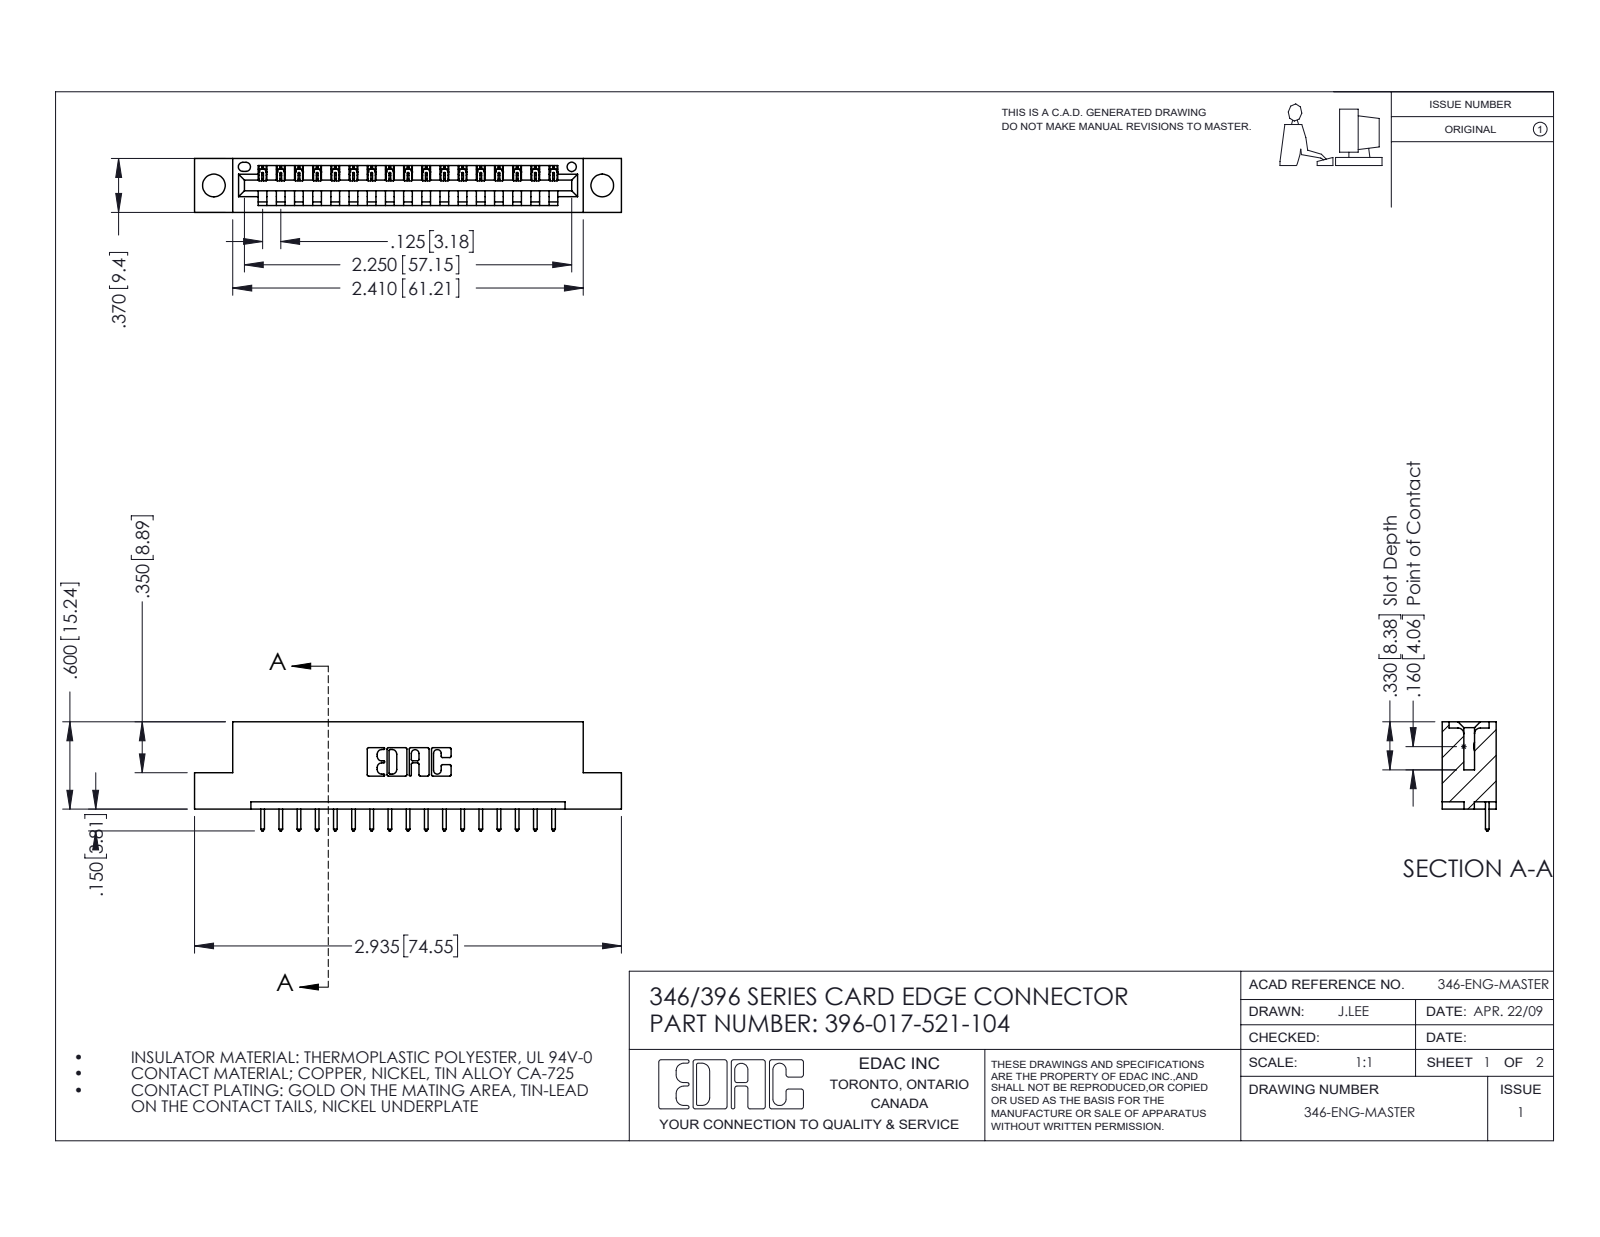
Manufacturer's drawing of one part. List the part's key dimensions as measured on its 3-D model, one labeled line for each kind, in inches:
Part name (STEP PRODUCT): 346 Part_Flush Mounting Lugs - 0.156 Dia-TH; 345-292-001_345-293-121; 396-017-521-104
STEP written by: SolidWorks 2016 (CONFIG_CONTROL_DESIGN)
Units: inches
Bodies: 18 solids, 1108 faces (756 planar, 352 cylindrical, 0 other)
Overall size (bounding box): 2.935 × 0.75 × 0.37
Volume: 0.417 in³ · Surface area: 12.21 in²
Round holes (diameter × count): ⌀0.156 ×2, ⌀0.064 ×1
Partial cylindrical surfaces — rounded edges, fillets, slot ends (radius × count): R0.006 ×34, R0.01 ×34, R0.01 ×22, R0.007 ×6, R0.031 ×6, R0.026 ×3, R0.031 ×2, R0.04 ×2
Main face-to-face distances: 0.048, 0.322, 0.25, 0.37, 0.072, 0.298, 0.025, 0.148, 0.222, 0.1
Hole centre spacings: 0.246, 2.463, 2.67
